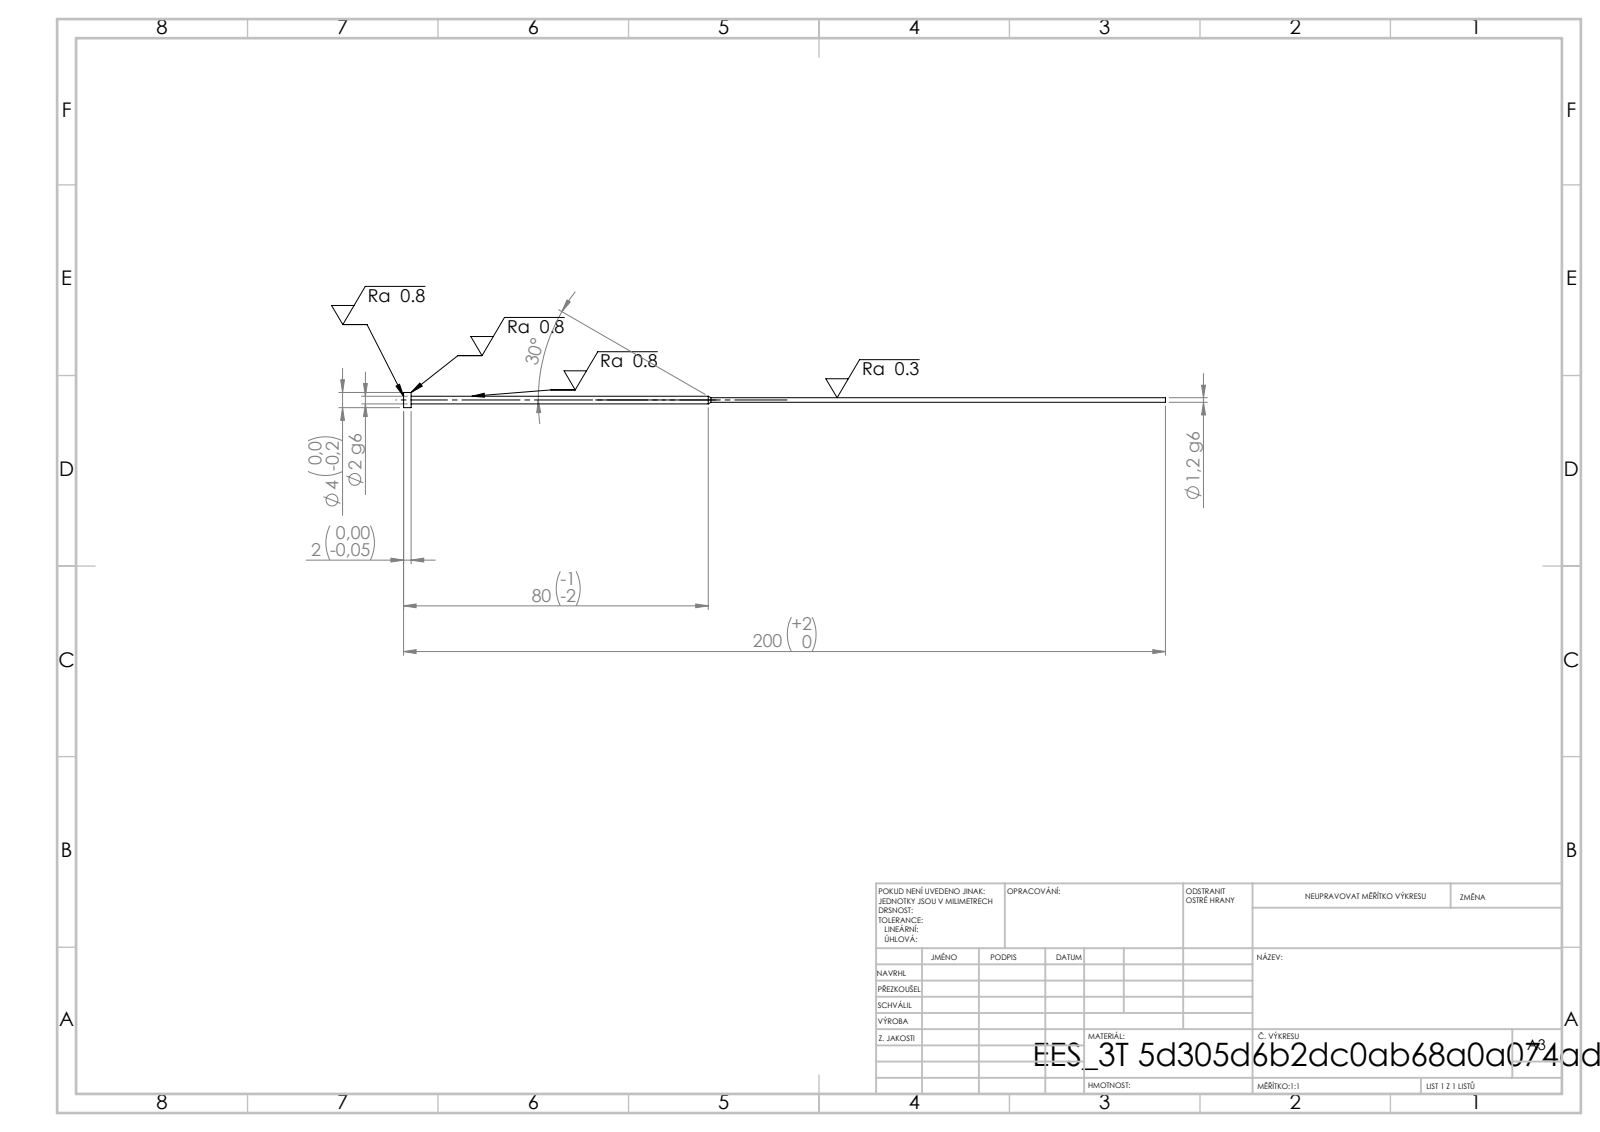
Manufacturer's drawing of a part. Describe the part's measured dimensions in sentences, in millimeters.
Its 3-D file was written by "SolidWorks 2019 (CONFIG_CONTROL_DESIGN)". It is 1 solid with 11 faces: 3 planar, 6 cylindrical and 2 other. Overall it measures 200 by 4 by 4 millimeters. Its volume is 407 cubic millimeters and its surface area 992 square millimeters. Round bosses or shafts: 1 of diameter 4, 1 of diameter 2, 1 of diameter 1.2. The main face-to-face distances are 2, 198, 200.
